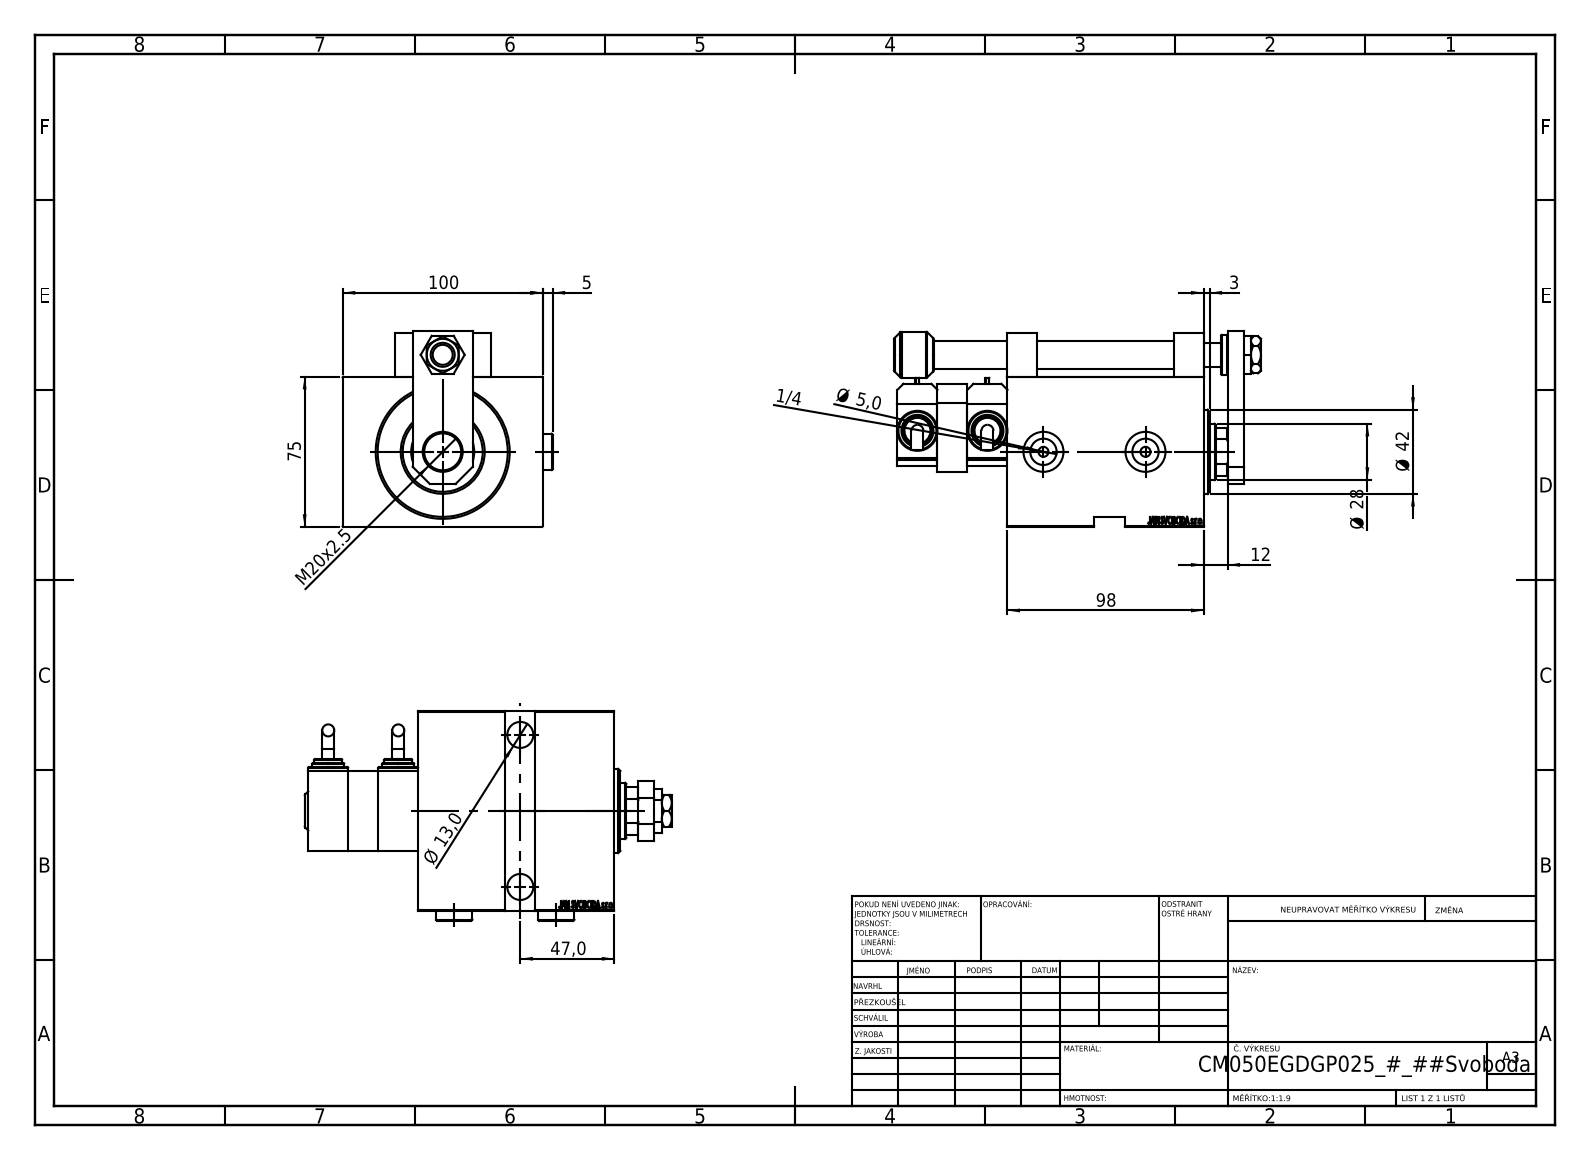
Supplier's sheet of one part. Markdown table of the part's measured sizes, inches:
| quantity | value |
| --- | --- |
| part name | TYC_P; SWITCH_P_FRONT_BACK; V450CM_E_VCP; NUT_D16 (+7 more) |
| STEP written by | SolidWorks 2019 (CONFIG_CONTROL_DESIGN) |
| units | inches |
| bodies | 16 solids, 1127 faces (556 planar, 118 cylindrical, 453 other) |
| overall size | 7.224 × 4.13 × 3.858 |
| volume | 50.35 in³ |
| surface area | 229.5 in² |
| round holes (diameter × count) | 0.157 × 4, 0.315 × 4, 0.512 × 3, 0.787 × 3, 0.197 × 2, 0.518 × 2, 0.748 × 2, 0.472 × 1, 0.551 × 1, 0.728 × 1, 1.102 × 1, 1.24 × 1 |
| round bosses / shafts (diameter × count) | 0.787 × 3, 0.709 × 2, 0.63 × 2, 0.551 × 2, 0.236 × 2, 2.047 × 1, 1.654 × 1, 0.906 × 1 |
| partial cylindrical surfaces (radius × count) | 0.118 × 1, 0.531 × 1 |
| main face-to-face distances | 1.378, 2.953, 0.197, 3.858, 0.787, 3.937, 4.646, 0.591, 2.756, 1.181 |
| hole center spacings | 0.787, 1.906, 2.037, 2.447, 2.55, 3.268, 3.361, 1.909 |
